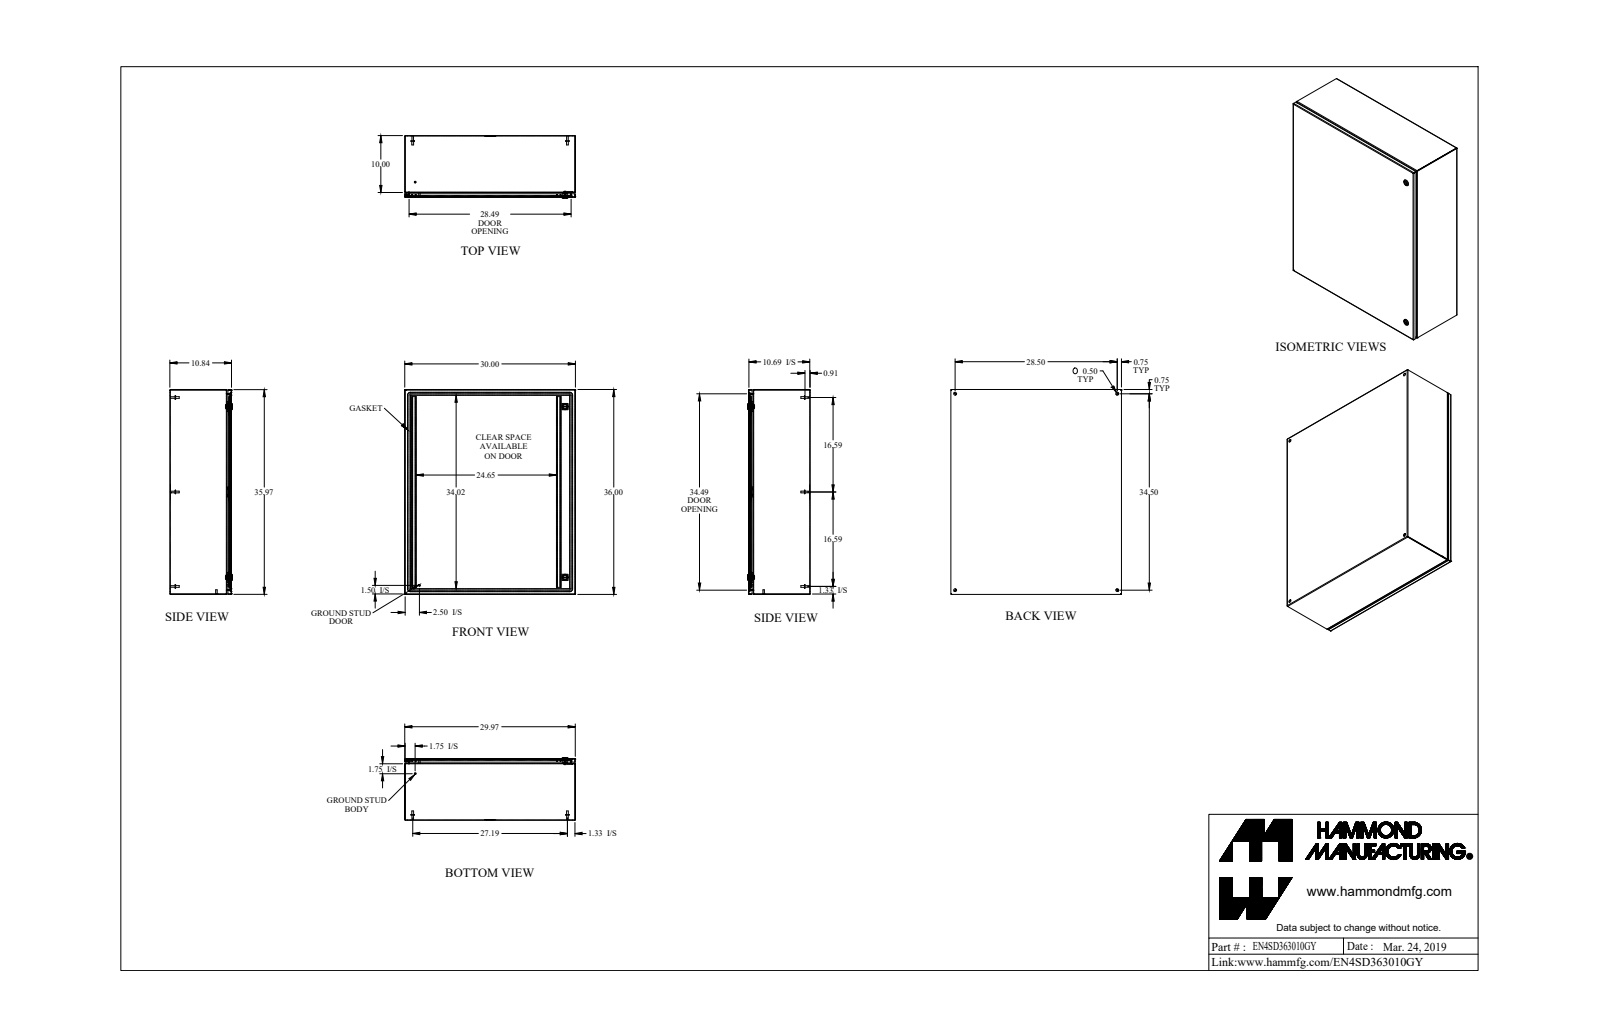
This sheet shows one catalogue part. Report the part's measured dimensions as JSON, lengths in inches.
{"part_name": "EN4SD363010GY", "step_written_by": "SolidWorks 2019 (AUTOMOTIVE_DESIGN)", "units": "inches", "bodies": {"solids": 33, "faces": 909, "planar": 430, "cylindrical": 295, "other": 184}, "overall_size": [36, 30, 10.997], "volume_in3": 286.5, "surface_area_in2": 8027, "round_holes": [[0.5, 4], [0.232, 2], [0.625, 2], [0.785, 2], [0.172, 1], [0.24, 1], [0.242, 1]], "round_bosses_or_shafts": [[0.625, 6], [0.313, 6], [0.27, 6], [1.1, 2], [0.525, 2], [0.281, 2], [0.25, 2], [0.455, 1]], "partial_cylinders_radius": [[0.036, 20], [0.108, 20], [0.043, 12], [0.081, 12], [0.312, 10], [0.006, 6], [0.062, 6], [0.125, 4]], "face_to_face_distances": [0.072, 10.765, 10.693, 10.837, 29.928, 35.928, 29.856, 30, 35.856, 36], "hole_center_spacings": [27.519, 28.5, 34.5, 44.749, 2.493, 2.494, 29.999, 32.267]}
